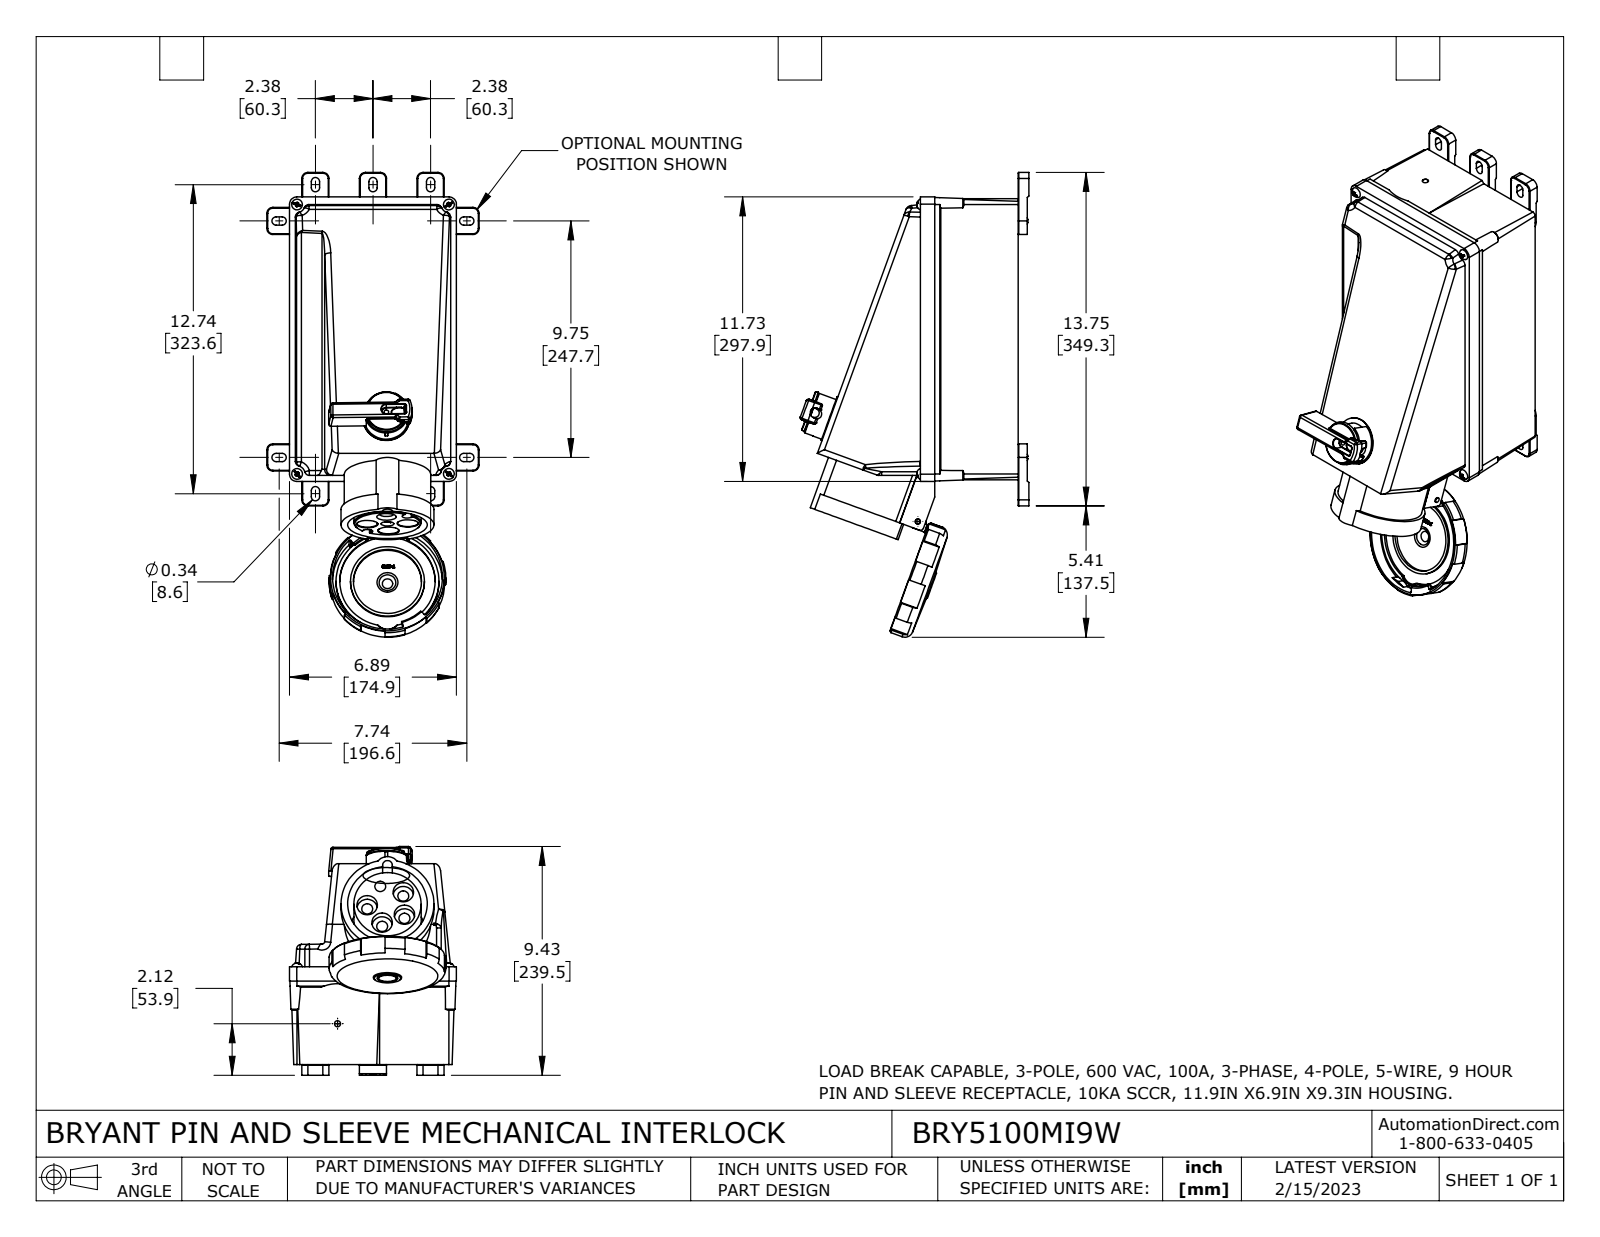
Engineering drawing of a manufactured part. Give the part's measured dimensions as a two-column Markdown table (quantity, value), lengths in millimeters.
| quantity | value |
| --- | --- |
| part name | BRY5100MI9W |
| STEP written by | SolidWorks 2021 (CONFIG_CONTROL_DESIGN) |
| units | millimeters |
| bodies | 13 solids, 1762 faces (633 planar, 574 cylindrical, 555 other) |
| overall size | 486.8 × 239.5 × 174.9 |
| volume | 7 908 000 mm³ |
| surface area | 562 500 mm² |
| round holes (diameter × count) | 7.1 × 5, 11.4 × 5, 21.4 × 4, 7.1 × 3, 6.4 × 2, 4.8 × 1, 5.3 × 1, 19.7 × 1, 21.8 × 1, 26.4 × 1, 71.3 × 1, 83.4 × 1 |
| round bosses / shafts (diameter × count) | 107.8 × 1, 77.4 × 1, 72 × 1, 70.5 × 1, 48.8 × 1, 31.6 × 1, 20.3 × 1, 19.3 × 1 |
| partial cylindrical surfaces (radius × count) | 0.4 × 115, 0.8 × 30, 2 × 30, 2.3 × 19, 6.4 × 19, 0.5 × 12, 1.9 × 12, 4.3 × 10 |
| main face-to-face distances | 87.4, 154.3, 153.4, 0.9, 294.5, 102.4, 15, 3, 3.8, 174.9 |
| hole center spacings | 40.4, 17.5, 21.2, 25, 25, 40.4, 40.4, 17.5 |
